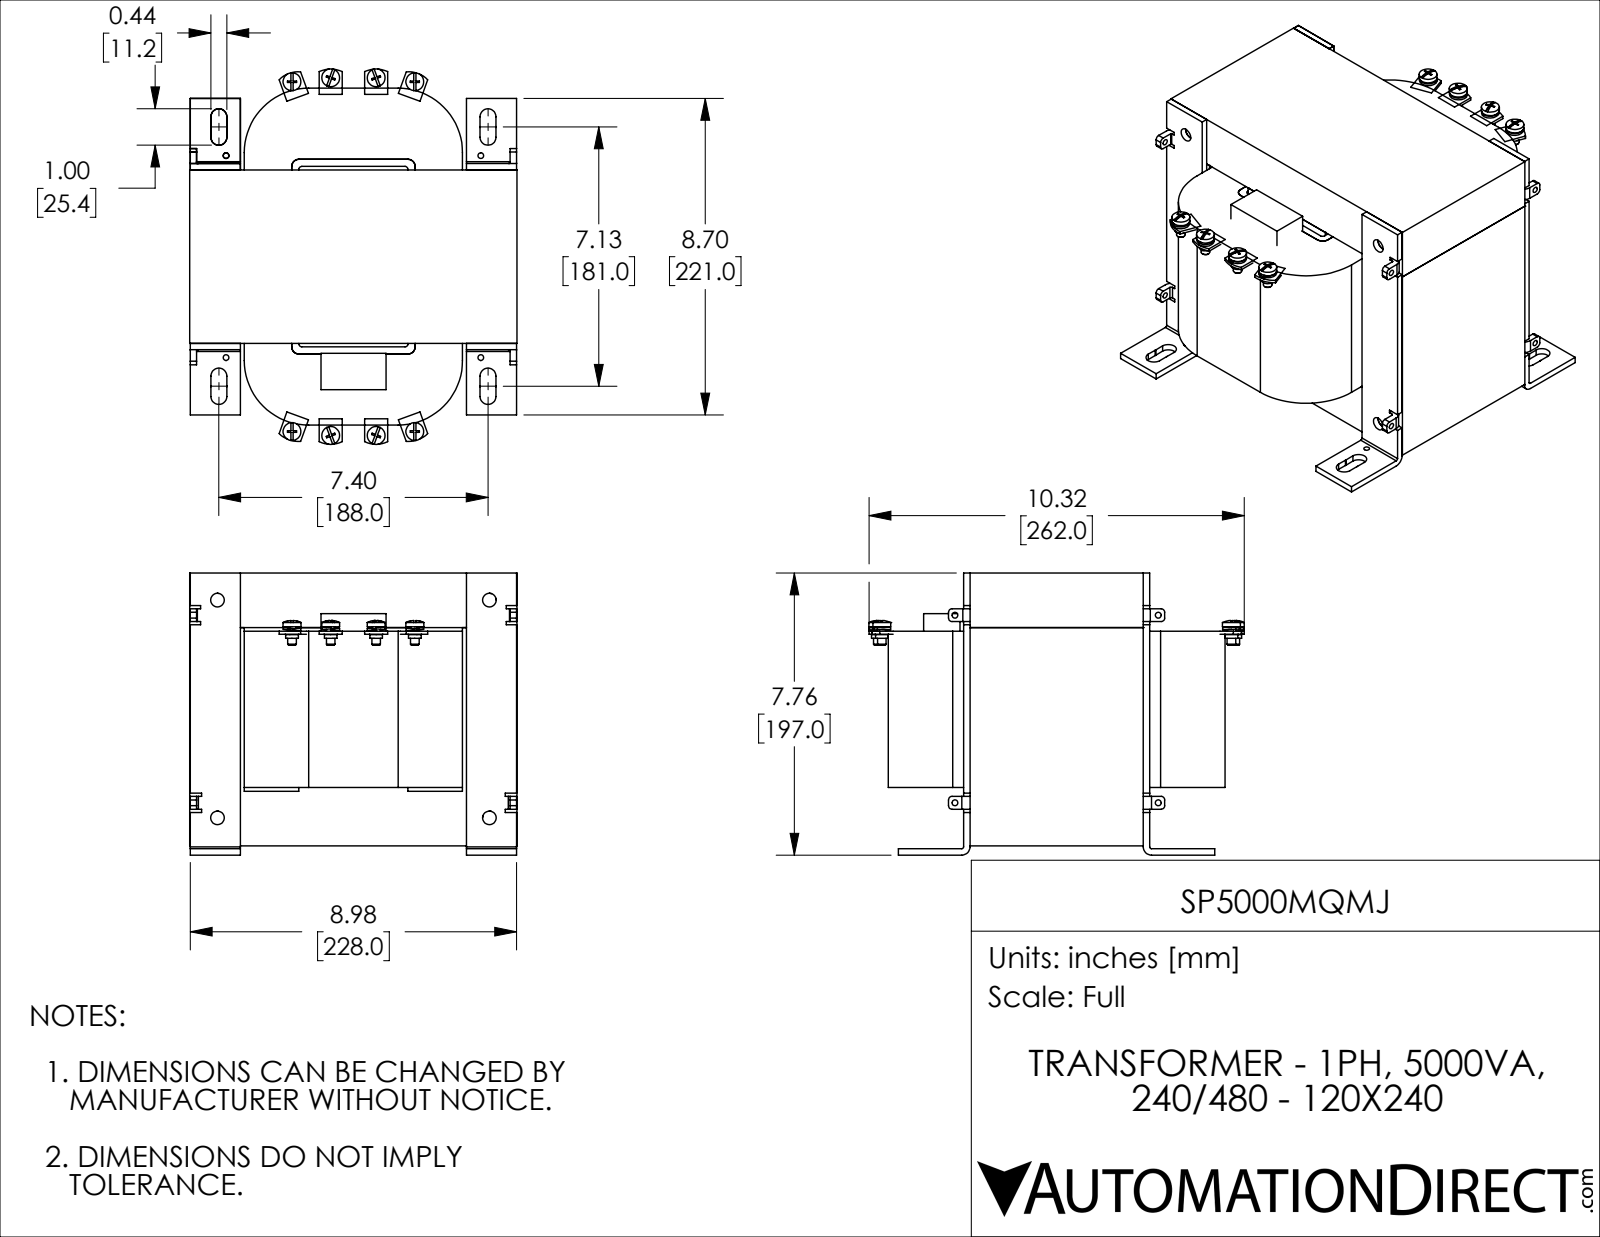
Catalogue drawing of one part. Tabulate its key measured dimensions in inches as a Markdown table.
| quantity | value |
| --- | --- |
| part name | SP5000MQMJ |
| STEP written by | SolidWorks 2018 (AUTOMOTIVE_DESIGN) |
| units | inches |
| bodies | 34 solids, 683 faces (366 planar, 209 cylindrical, 108 other) |
| overall size | 10.322 × 9 × 7.756 |
| volume | 432.7 in³ |
| surface area | 1 053 in² |
| round holes (diameter × count) | 0.25 × 8, 0.157 × 4, 0.161 × 4, 0.374 × 4 |
| round bosses / shafts (diameter × count) | 0.492 × 8, 0.346 × 8, 0.236 × 8 |
| partial cylindrical surfaces (radius × count) | 0.098 × 8, 0.22 × 8, 0.732 × 8, 0.05 × 6, 0.227 × 6, 0.02 × 4, 0.197 × 4, 0.221 × 4 |
| main face-to-face distances | 1.5, 6, 7.5, 3, 0.197, 4.5, 1.303, 4.697, 3.197, 1.604 |
| hole center spacings | 1.07, 2.316, 2.724, 3.587, 4.65, 5.576, 7.797, 8.212 |
